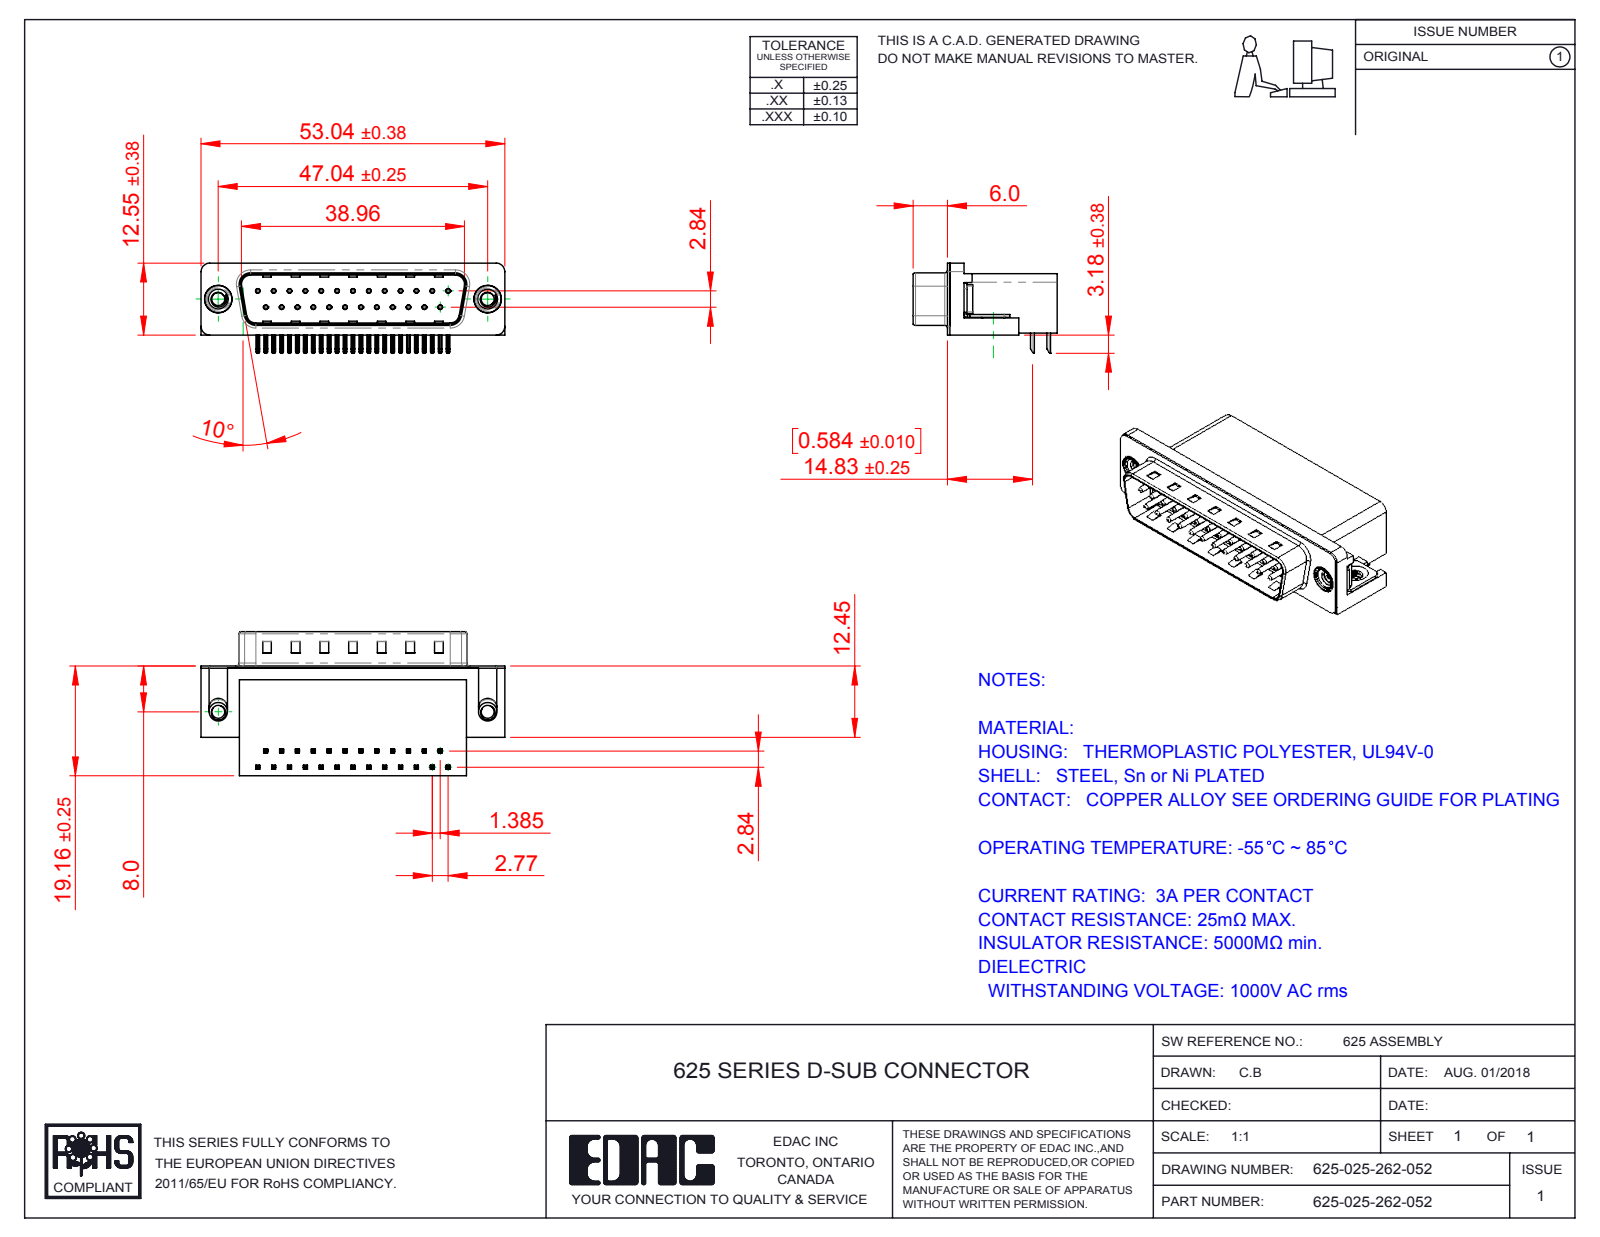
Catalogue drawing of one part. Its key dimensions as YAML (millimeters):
part_name: "625 Shell_25 Socket; 625 4-40 Threaded Board Mount; 625 Contact Bottom; 625 Contact Top (+3 more)"
step_written_by: "SolidWorks 2016 (CONFIG_CONTROL_DESIGN)"
units: millimeters
bodies: {solids: 31, faces: 2297, planar: 1407, cylindrical: 673, other: 217}
overall_size: [53.04, 25.16, 15.73]
volume: 9177
surface_area: 8941
round_holes:
  - {diameter: 0.35, count: 25}
  - {diameter: 0.8, count: 25}
  - {diameter: 2.26, count: 4}
  - {diameter: 4, count: 2}
  - {diameter: 4.8, count: 2}
  - {diameter: 5, count: 2}
round_bosses_or_shafts:
  - {diameter: 0.75, count: 25}
  - {diameter: 4.9, count: 2}
  - {diameter: 4.75, count: 2}
  - {diameter: 3.9, count: 2}
  - {diameter: 3.26, count: 2}
partial_cylinders:
  - {radius: 0.25, count: 108}
  - {radius: 0.12, count: 50}
  - {radius: 1, count: 16}
  - {radius: 0.5, count: 9}
  - {radius: 1.6, count: 8}
  - {radius: 1.5, count: 7}
  - {radius: 0.9, count: 4}
  - {radius: 2, count: 4}
face_to_face_distances: [0.4, 10.35, 18.76, 2.1, 8.76, 10.46, 10.86, 1.7, 19.16, 10.11]
hole_center_spacings: [3.16, 2.77, 11.08, 5.54, 8.31, 5.03, 13.85, 7.48]
